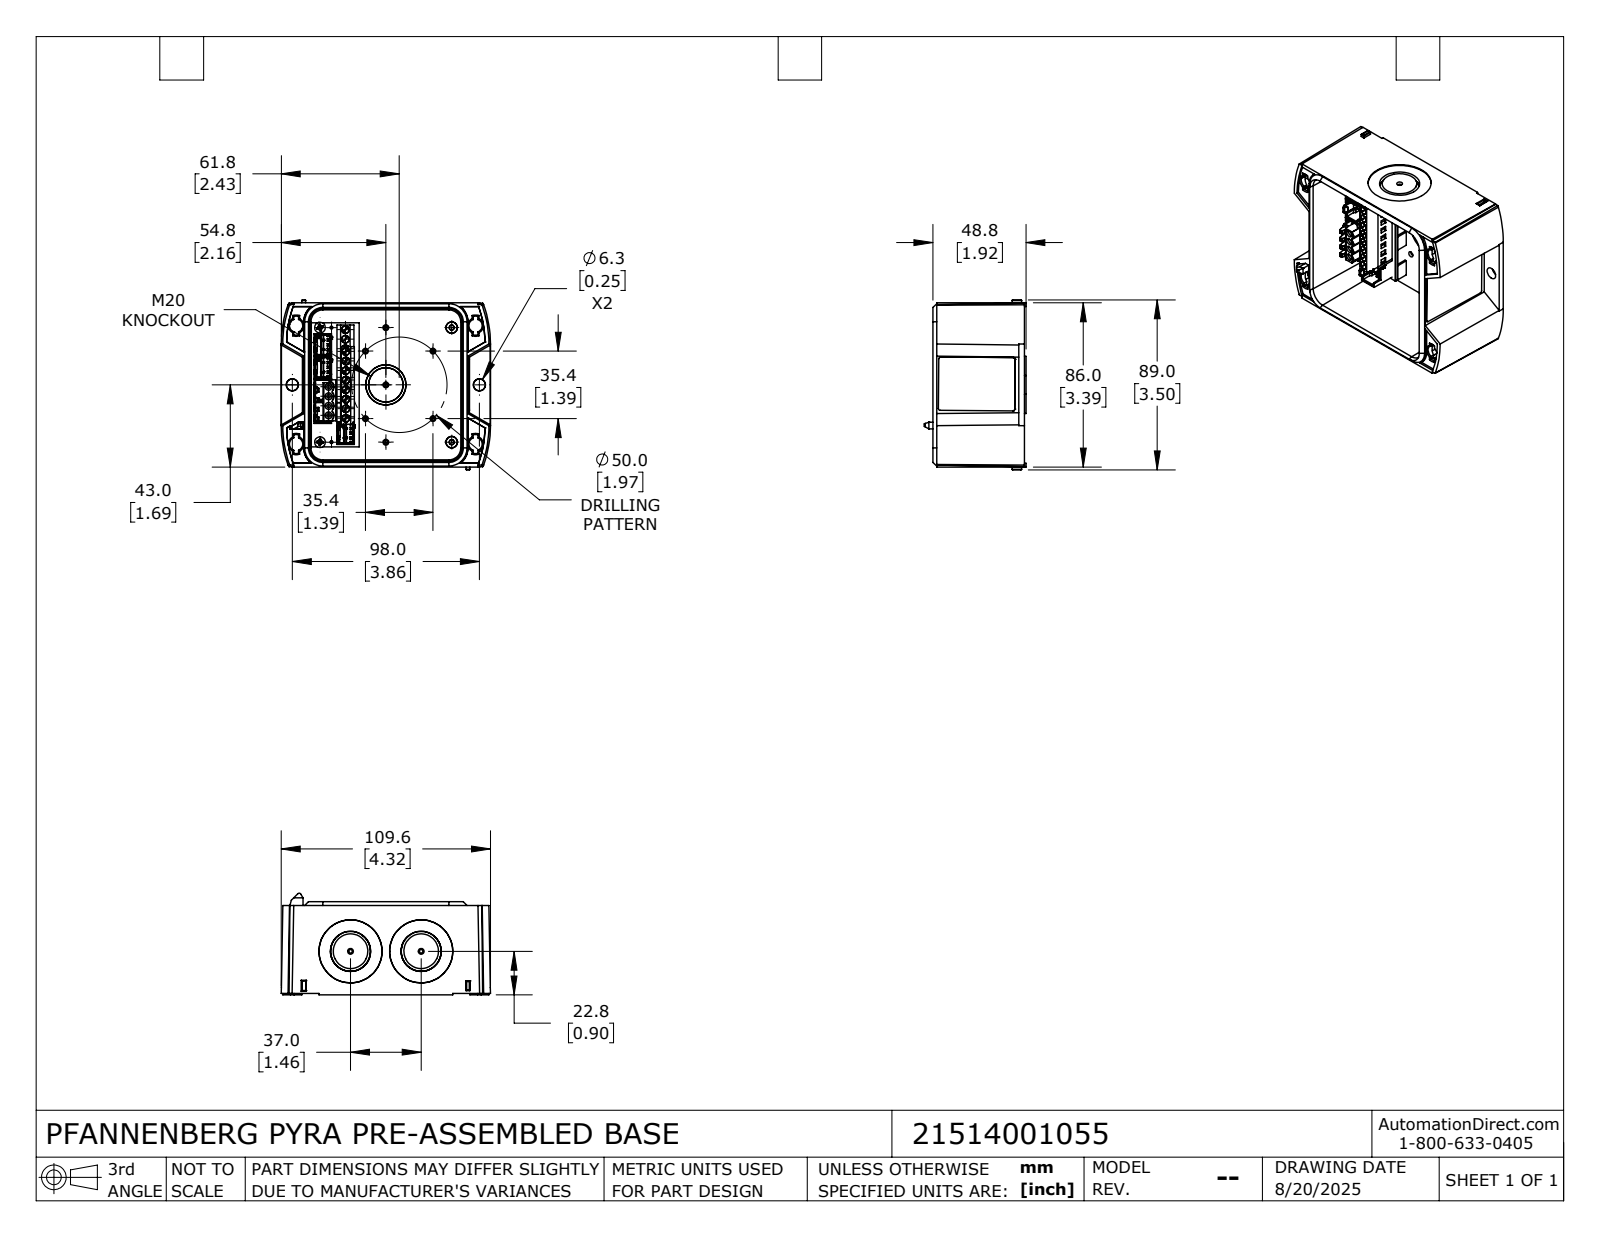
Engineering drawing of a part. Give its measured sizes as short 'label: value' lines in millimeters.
name: 21514001055
written by: SolidWorks 2024 (CONFIG_CONTROL_DESIGN)
unit: mm
bodies: 17 solids, 2300 faces (1680 planar, 367 cylindrical, 253 other)
size: 109.61 × 89 × 53.28
volume: 112 033 mm³; area: 89 860 mm²
holes: 18× ⌀4, 10× ⌀1, 10× ⌀1.4, 5× ⌀1.9, 4× ⌀1.8, 4× ⌀2.3, 4× ⌀3.6, 2× ⌀1.5, 2× ⌀3
bosses: 18× ⌀3.8, 5× ⌀1.8, 2× ⌀5.6, 2× ⌀2.9
rounds: 16× R0.3, 15× R1, 14× R0.4, 10× R0.5, 5× R2.9, 3× R9
face distances: 3, 6.5, 9.5, 11, 86, 8, 83, 1.5, 11.1, 1.6
hole spacings: 5, 10, 15, 11, 16, 20, 21, 6.01
